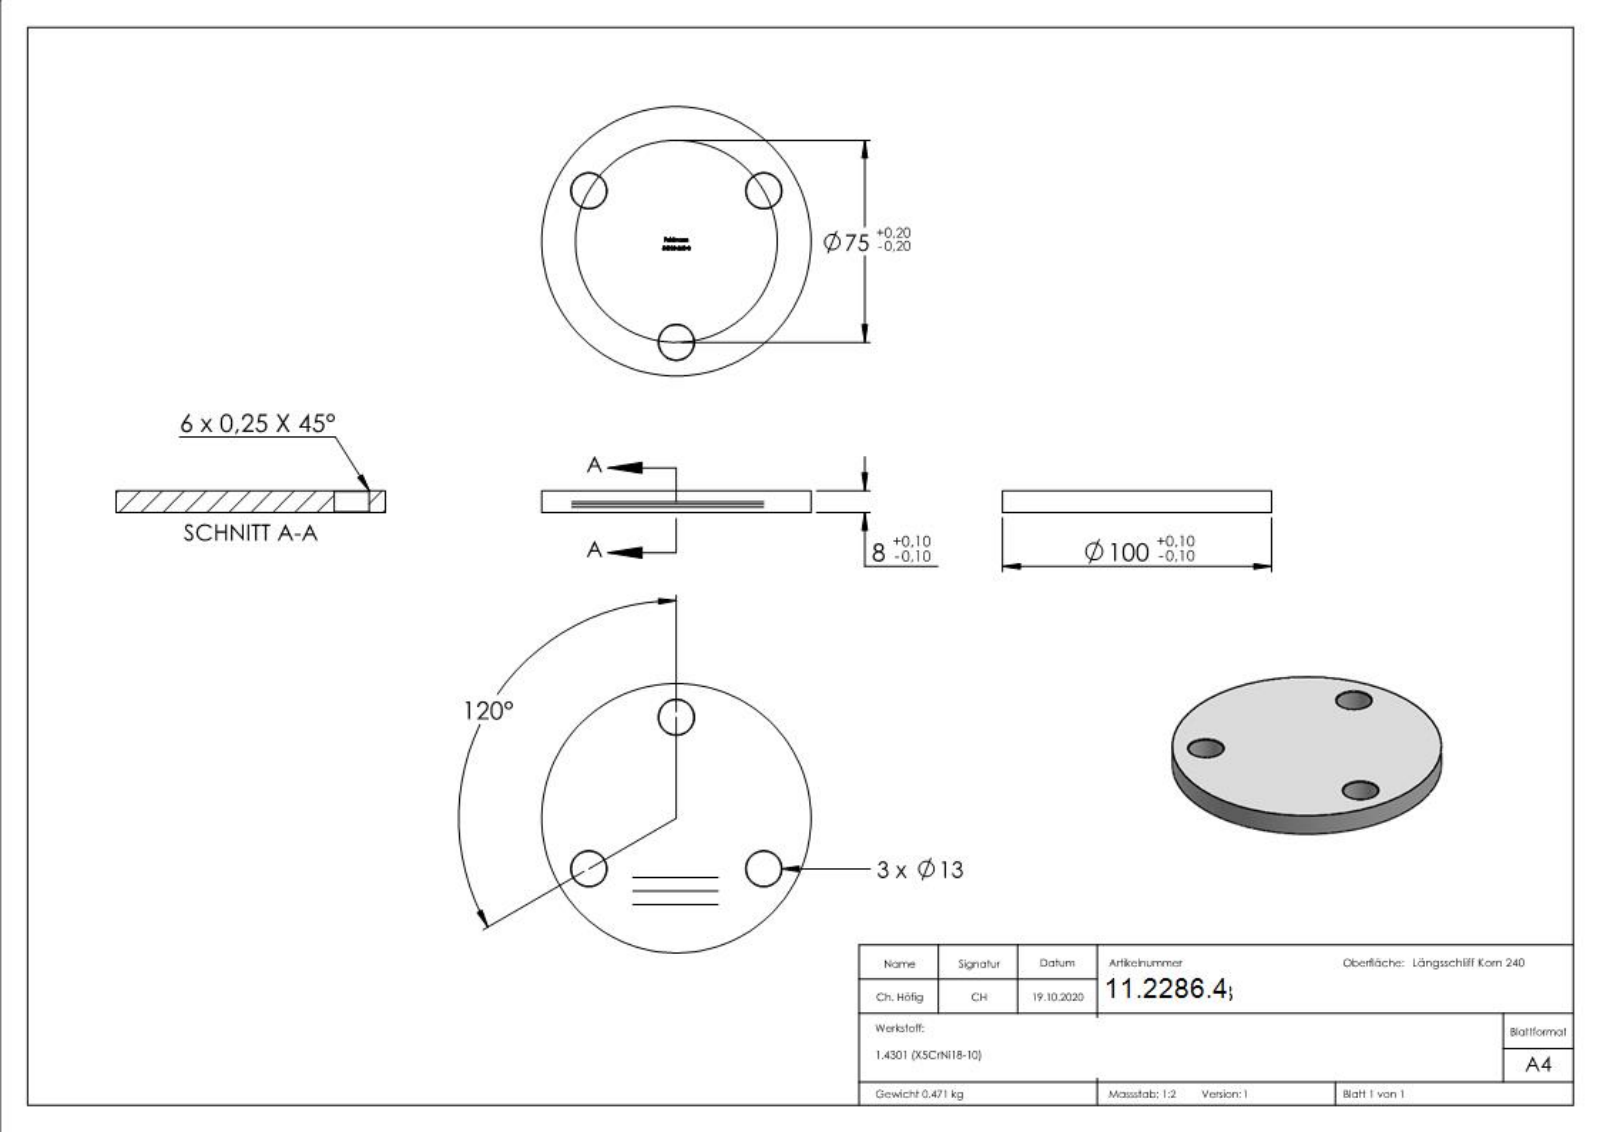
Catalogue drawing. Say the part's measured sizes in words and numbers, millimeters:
The part is named "54103-240-8". Its 3-D file was written by "SolidWorks 2018 (CONFIG_CONTROL_DESIGN)". It is 1 solid with 270 faces: 139 planar, 8 cylindrical and 123 other. Overall it measures 100 by 100 by 8 millimeters. Its volume is 59 638 cubic millimeters and its surface area 18 380 square millimeters. Round holes: 3 of diameter 13. Round bosses or shafts: 1 of diameter 100. The main face-to-face distances are 8, 7.9, 0.44, 2.97, 3.21, 1.12, 0.39, 3.19, 3.39, 1.58. The hole center spacings are 64.95, 64.96.
